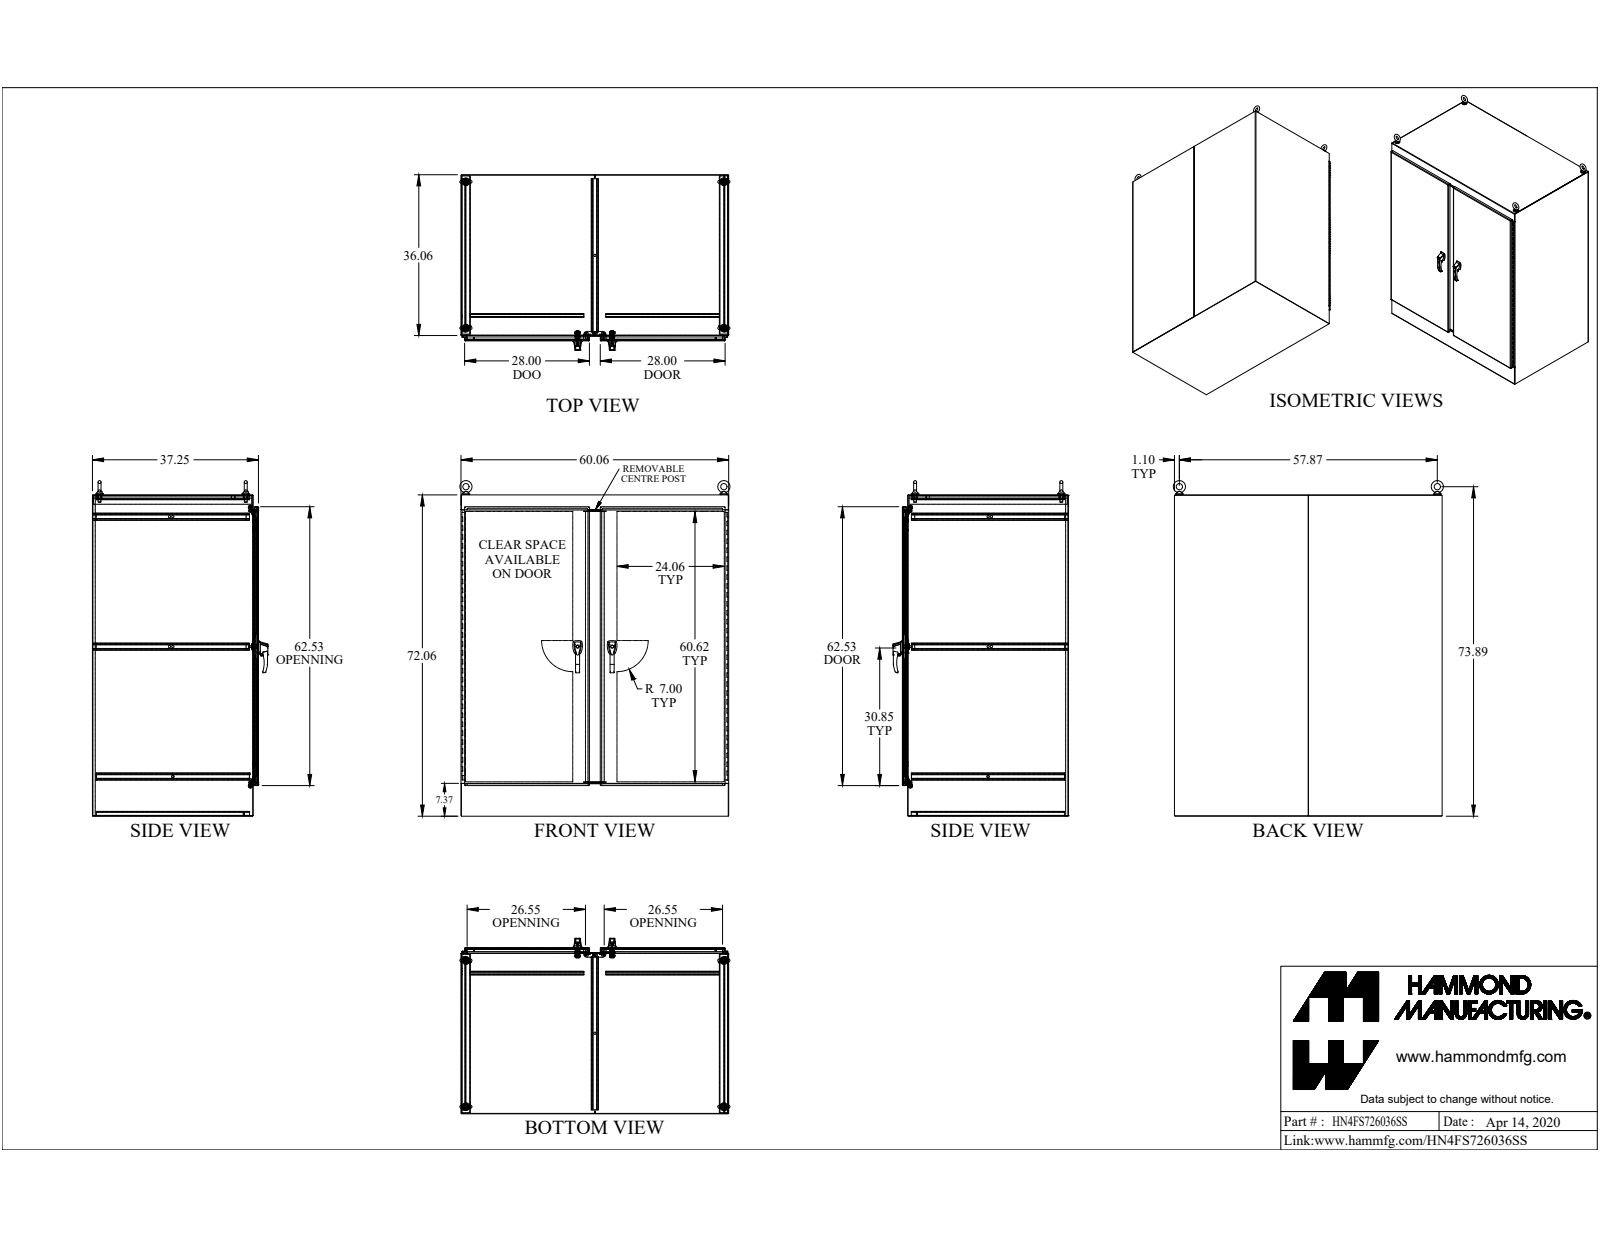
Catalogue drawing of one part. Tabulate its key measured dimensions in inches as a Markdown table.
| quantity | value |
| --- | --- |
| part name | HN4FS726036SS |
| STEP written by | SolidWorks 2019 (CONFIG_CONTROL_DESIGN) |
| units | inches |
| bodies | 114 solids, 3025 faces (1591 planar, 1174 cylindrical, 260 other) |
| overall size | 75.256 × 60.604 × 39.362 |
| volume | 2 087 in³ |
| surface area | 44 079 in² |
| round holes (diameter × count) | 0.304 × 20, 0.35 × 8, 0.25 × 7, 0.5 × 7, 0.75 × 6, 0.257 × 4, 0.28 × 4, 0.281 × 4, 0.313 × 4, 0.39 × 4, 0.413 × 4, 0.527 × 4 |
| round bosses / shafts (diameter × count) | 1.75 × 4, 1.5 × 4, 1.25 × 4, 1 × 4, 0.75 × 4, 0.63 × 4, 0.625 × 4, 0.624 × 4 |
| partial cylindrical surfaces (radius × count) | 0.043 × 54, 0.138 × 48, 0.5 × 33, 0.1 × 28, 0.125 × 27, 0.018 × 24, 0.06 × 24, 0.318 × 18 |
| main face-to-face distances | 0.095, 37.152, 59.965, 71.965, 37.057, 37.247, 59.87, 60.06, 71.87, 72.06 |
| hole center spacings | 6, 58.636, 12, 59.55, 18, 61.043, 24, 63.073 |
